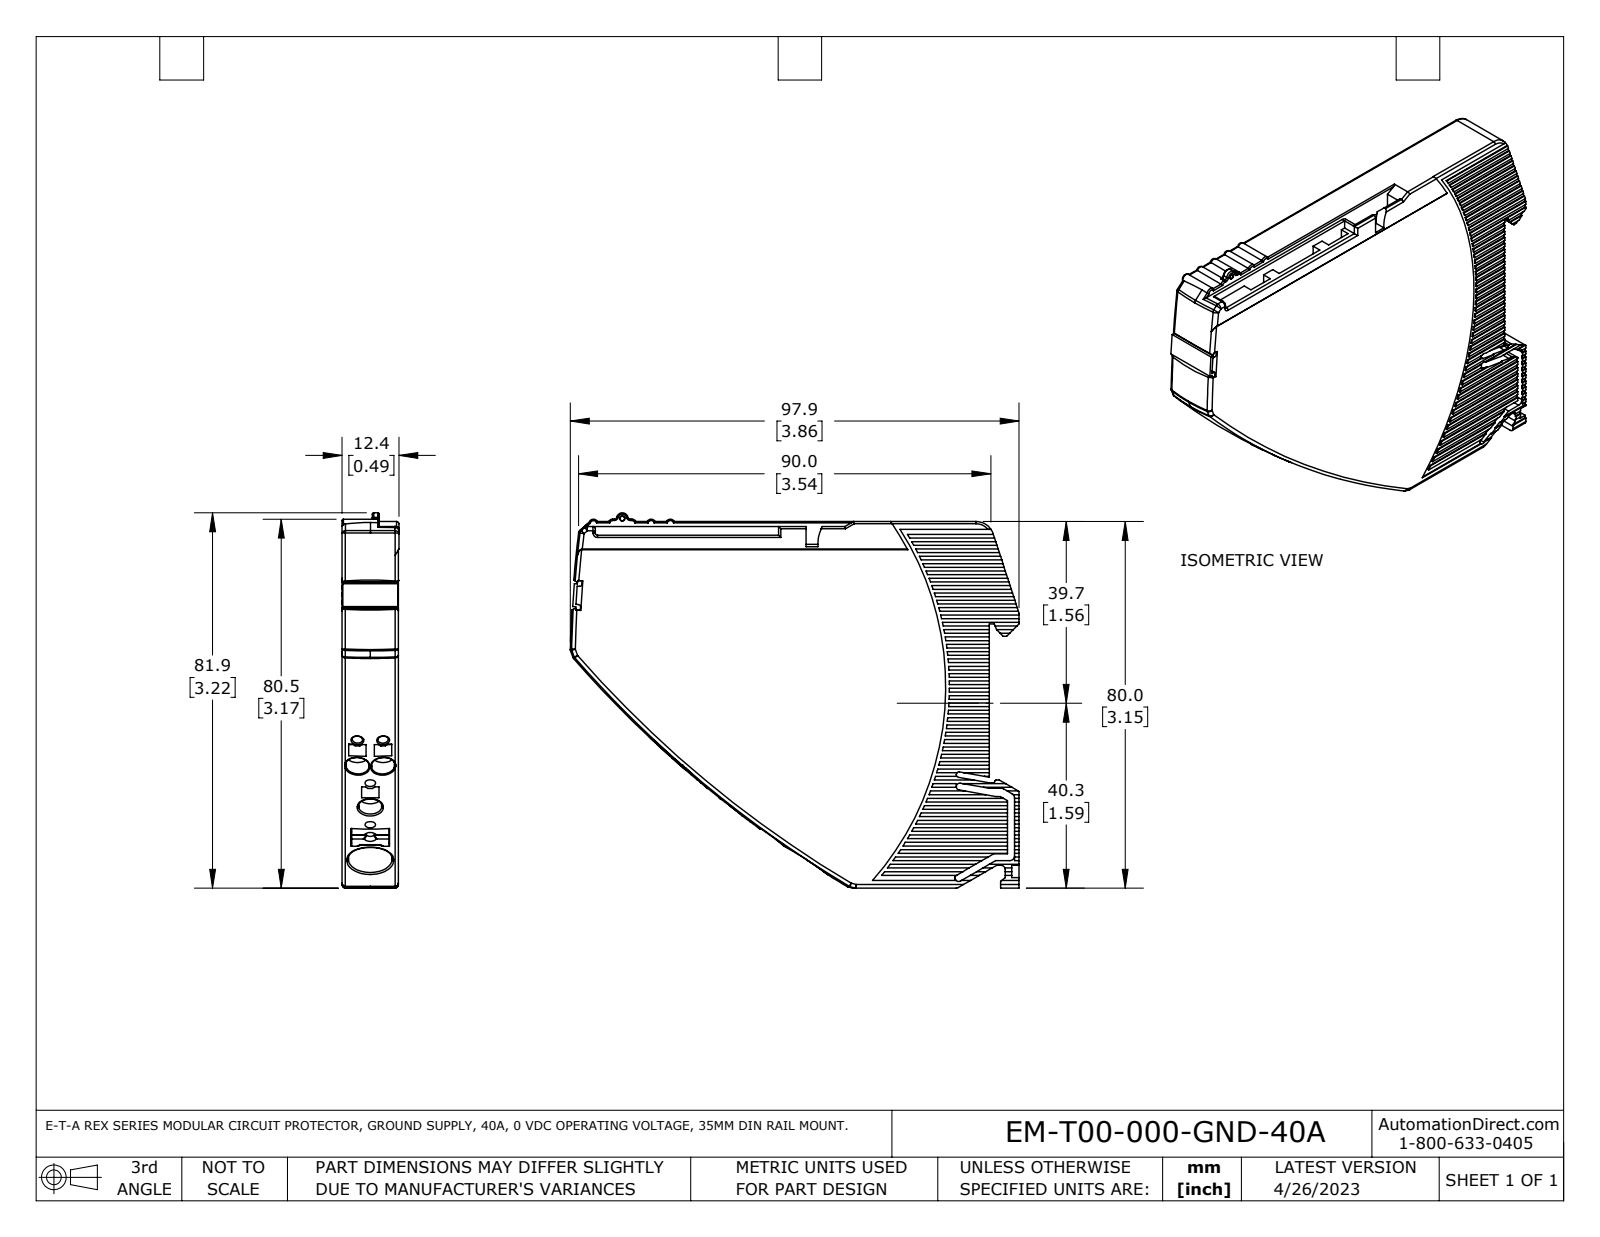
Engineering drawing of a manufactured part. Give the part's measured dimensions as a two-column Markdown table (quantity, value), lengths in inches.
| quantity | value |
| --- | --- |
| part name | t-em12-t00-000-gnd_ik00_REV2 |
| STEP written by | SolidWorks 2021 (AUTOMOTIVE_DESIGN) |
| units | inches |
| bodies | 1 solid, 907 faces (618 planar, 187 cylindrical, 102 other) |
| overall size | 3.856 × 3.224 × 0.488 |
| volume | 4.339 in³ |
| surface area | 30.48 in² |
| round holes (diameter × count) | 0.091 × 4, 0.039 × 1 |
| partial cylindrical surfaces (radius × count) | 0.02 × 12, 0.039 × 11, 0.031 × 9, 0.098 × 6, 0.012 × 5, 0.021 × 4, 0.008 × 3, 0.006 × 2 |
| main face-to-face distances | 0.484, 0.476, 0.469, 0.039, 0.098, 0.059, 0.126, 0.157, 0.134, 0.35 |
| hole center spacings | 0.22, 0.562, 0.562 |
